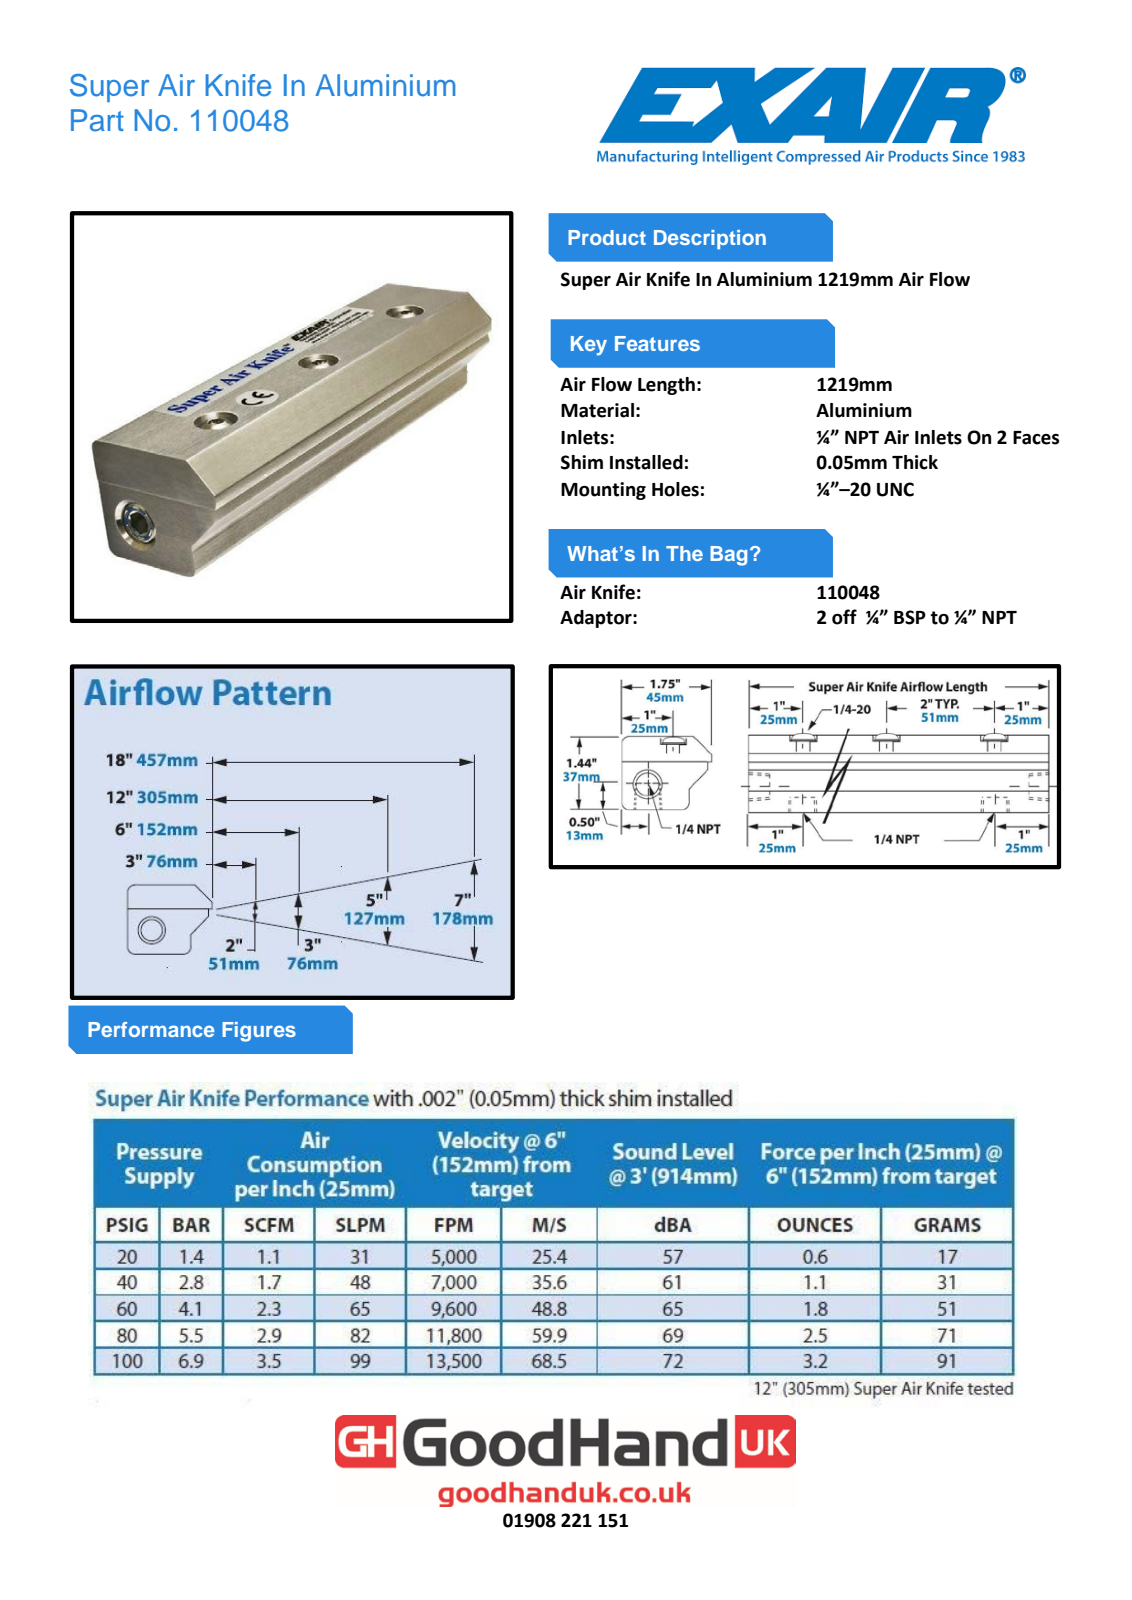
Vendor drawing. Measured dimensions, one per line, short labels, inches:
name: 110048; 1100481; 1100482; 1100483 (+8 more)
written by: Autodesk Inventor 2012 (AUTOMOTIVE_DESIGN)
unit: in
bodies: 22 solids, 413 faces (244 planar, 121 cylindrical, 48 other)
size: 48 × 1.749 × 1.452
volume: 102.3 in³; area: 492.3 in²
holes: 25× ⌀0.5, 24× ⌀0.201, 24× ⌀0.282, 3× ⌀0.433, 1× ⌀0.437
bosses: 20× ⌀0.437, 20× ⌀0.25
rounds: 3× R0.125
face distances: 0.5, 0.937, 1.437, 1.313, 0.375, 1.687, 0.062, 0.437, 1.75, 0.125
hole spacings: 2, 4, 6, 8, 10, 12, 14, 16
